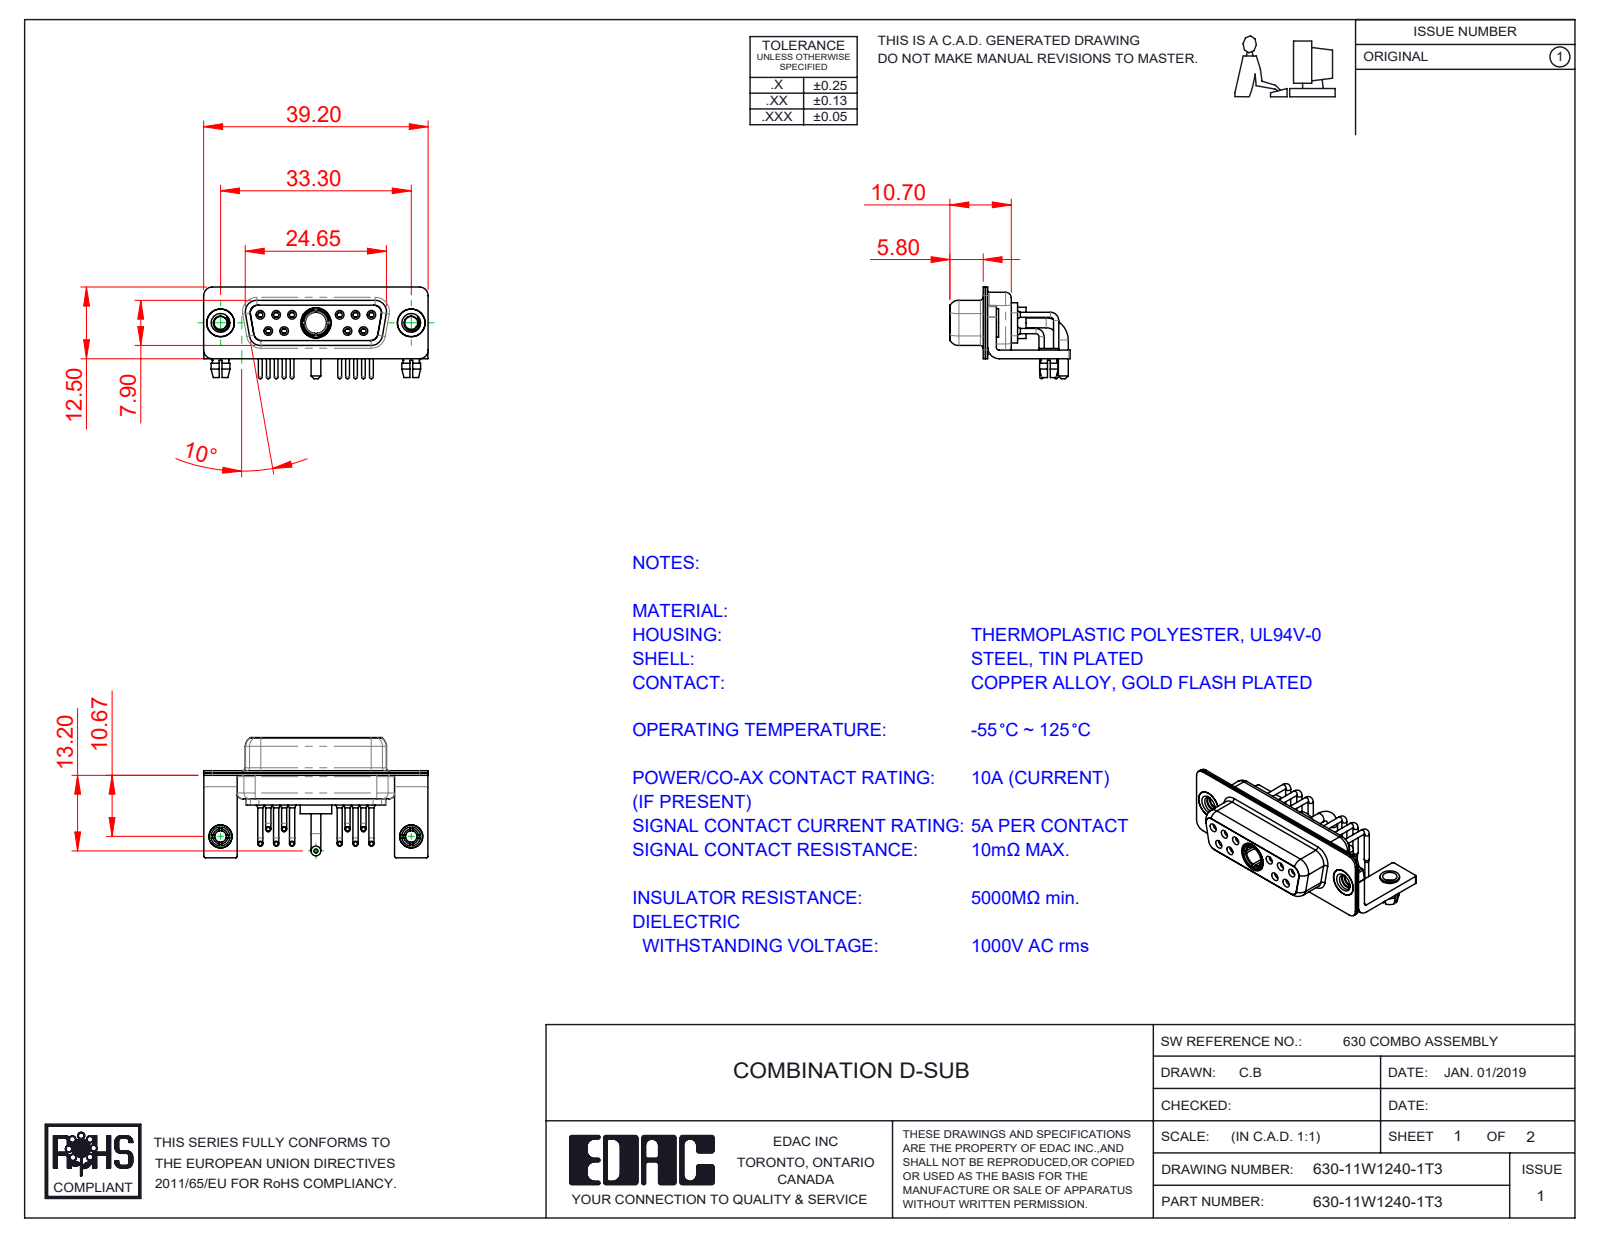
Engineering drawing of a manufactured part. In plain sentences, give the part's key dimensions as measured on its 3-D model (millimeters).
The part is named "Power Socket_10A RA; 630Combo Shell Front_15 Contacts; 630Combo Stabilizer Bracket; 630Combo Contact Row 1 (+6 more)". Its 3-D file was written by "SolidWorks 2020 (CONFIG_CONTROL_DESIGN)". It is 21 solids with 1019 faces: 314 planar, 442 cylindrical and 263 other. Overall it measures 39.2 by 21 by 16 millimeters. Its volume is 2 892 cubic millimeters and its surface area 7 018 square millimeters. Round holes: 12 of diameter 2, 10 of diameter 0.9, 10 of diameter 1.1, 10 of diameter 1.5, 6 of diameter 1.7, 4 of diameter 1.6, 3 of diameter 4.85, 2 of diameter 2.26, 2 of diameter 2.5, 2 of diameter 3.2, 2 of diameter 4, 2 of diameter 4.05. Round bosses or shafts: 10 of diameter 0.9, 10 of diameter 0.65, 6 of diameter 1.6, 2 of diameter 5, 2 of diameter 4.95, 2 of diameter 4.8, 2 of diameter 4, 2 of diameter 3.4. Partial cylindrical surfaces (rounded edges, fillets, slot ends): 16 of radius 0.25, 16 of radius 1.5, 13 of radius 2, 12 of radius 1.35, 8 of radius 1.6, 5 of radius 0.5, 4 of radius 0.6, 4 of radius 0.65. The main face-to-face distances are 0.4, 0.8, 0.45, 1.4, 8.45, 1.5, 1.8, 8.9, 6.2, 2.3. The hole center spacings are 3.16, 2.77, 13.85, 11.08, 16.62, 5.03, 5.04, 5.54.
